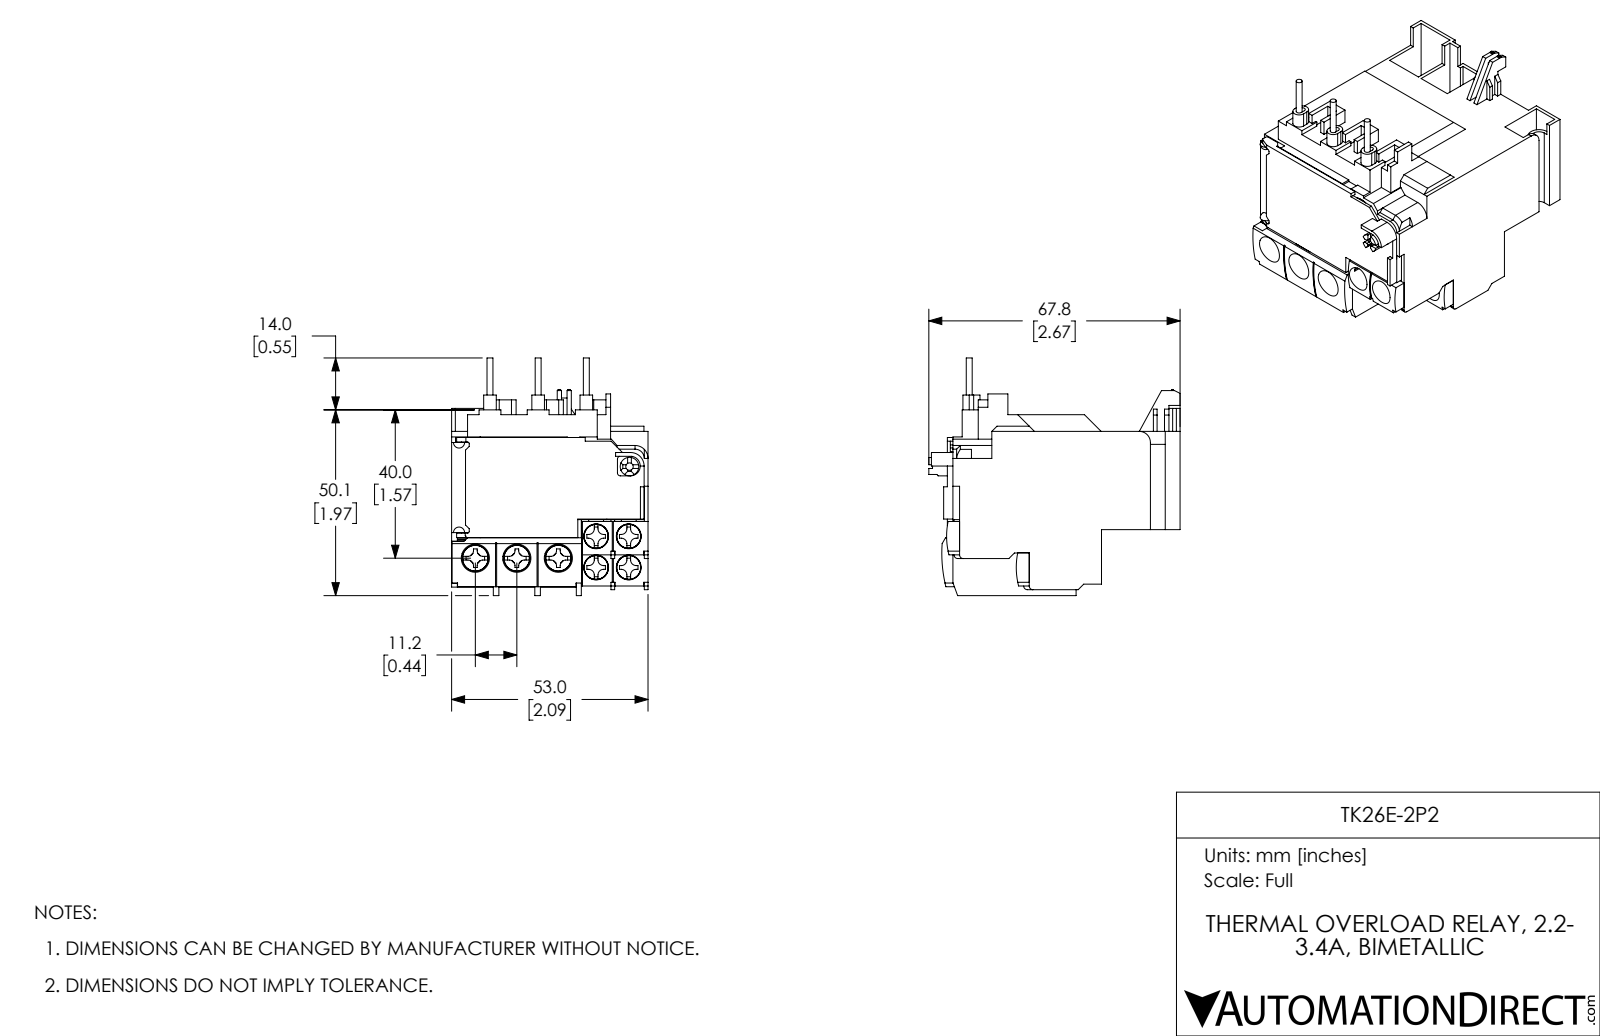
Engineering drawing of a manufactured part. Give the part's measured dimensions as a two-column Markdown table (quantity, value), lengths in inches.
| quantity | value |
| --- | --- |
| part name | TK26E-2P2 |
| STEP written by | SolidWorks 2017 (AUTOMOTIVE_DESIGN) |
| units | inches |
| bodies | 38 solids, 1480 faces (1225 planar, 220 cylindrical, 35 other) |
| overall size | 2.669 × 2.524 × 2.087 |
| volume | 6.099 in³ |
| surface area | 60.15 in² |
| round holes (diameter × count) | 0.138 × 4, 0.142 × 4, 0.264 × 4, 0.157 × 3, 0.161 × 3, 0.299 × 3, 0.039 × 1, 0.079 × 1, 0.197 × 1, 0.433 × 1 |
| round bosses / shafts (diameter × count) | 0.26 × 4, 0.063 × 3, 0.236 × 1 |
| partial cylindrical surfaces (radius × count) | 0.059 × 28, 0.039 × 8, 0.02 × 6, 0.067 × 6, 0.031 × 5, 0.047 × 4, 0.171 × 4, 0.189 × 3 |
| main face-to-face distances | 0.039, 0.354, 0.059, 0.472, 2.087, 0.079, 0.394, 0.433, 0.343, 0.028 |
| hole center spacings | 0.331, 0.346, 0.441, 0.479, 0.376, 0.413, 0.464, 0.74 |
